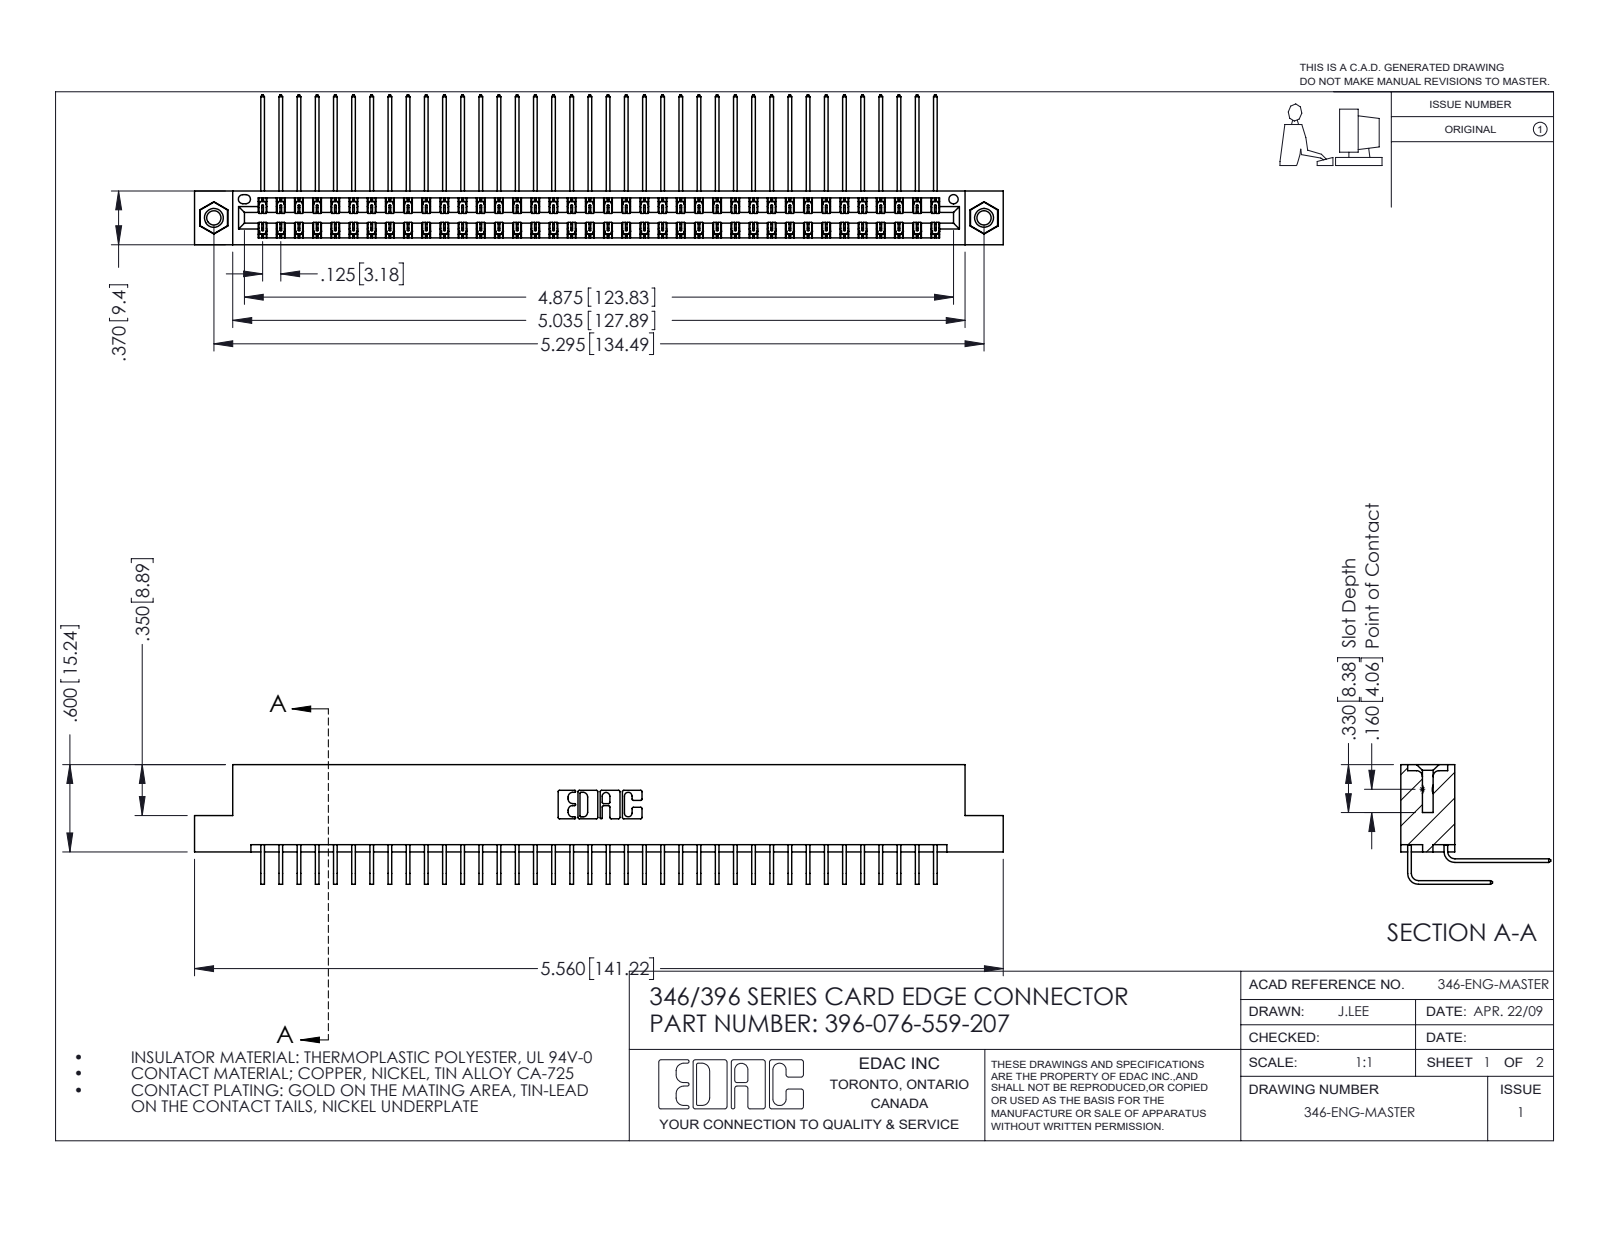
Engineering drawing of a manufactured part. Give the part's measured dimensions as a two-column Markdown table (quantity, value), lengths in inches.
| quantity | value |
| --- | --- |
| part name | 345-250-001_345-250-005-103; 346 Part_Flush Mounting Lugs - 0.156 Dia-TI; 396-076-559-207; 345-292-001_558 559 Tail - 1 (+1 more) |
| STEP written by | SolidWorks 2016 (CONFIG_CONTROL_DESIGN) |
| units | inches |
| bodies | 79 solids, 4286 faces (2920 planar, 1350 cylindrical, 16 other) |
| overall size | 5.56 × 1.03 × 0.823 |
| volume | 0.864 in³ |
| surface area | 33.39 in² |
| round holes (diameter × count) | 0.098 × 2, 0.125 × 2, 0.156 × 2, 0.064 × 1 |
| round bosses / shafts (diameter × count) | 0.155 × 2 |
| partial cylindrical surfaces (radius × count) | 0.006 × 114, 0.01 × 22, 0.007 × 6, 0.031 × 6, 0.026 × 3, 0.014 × 2, 0.022 × 2, 0.024 × 2 |
| main face-to-face distances | 0.048, 0.322, 0.025, 0.37, 0.25, 0.072, 0.298, 0.275, 0.148, 0.222 |
| hole center spacings | 0.246, 5.086, 5.295 |
